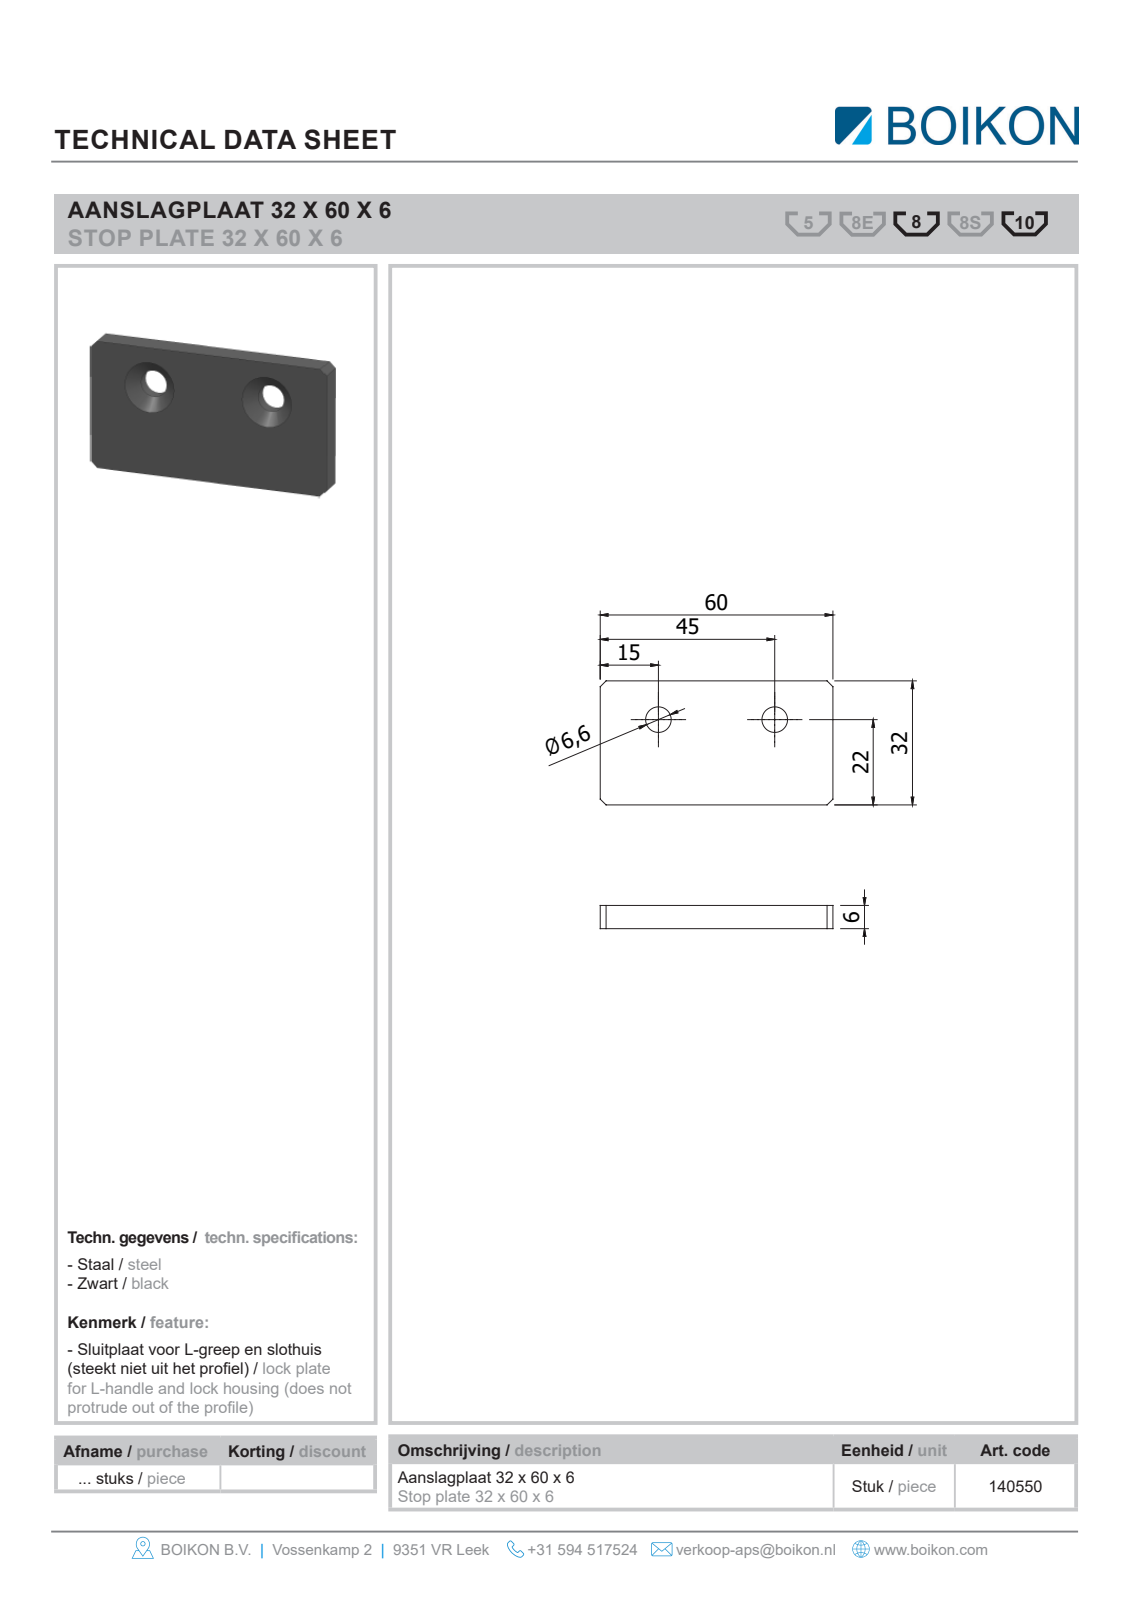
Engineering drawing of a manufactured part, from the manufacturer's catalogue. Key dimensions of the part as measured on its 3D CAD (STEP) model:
Part name (STEP PRODUCT): Root; 140550Tegenhoudplaatje 32x60x6BOIKON
STEP written by: HiCAD 2013 1802.4 Build 509 (AUTOMOTIVE_DESIGN)
Units: millimetres
Bodies: 1 solid, 14 faces (10 planar, 2 cylindrical, 2 other)
Overall size (bounding box): 60 × 32 × 6
Volume: 10 839 mm³ · Surface area: 4 976 mm²
Round holes (diameter × count): ⌀6.6 ×2
Main face-to-face distances: 6, 32, 60, 62.92
Hole centre spacings: 30
